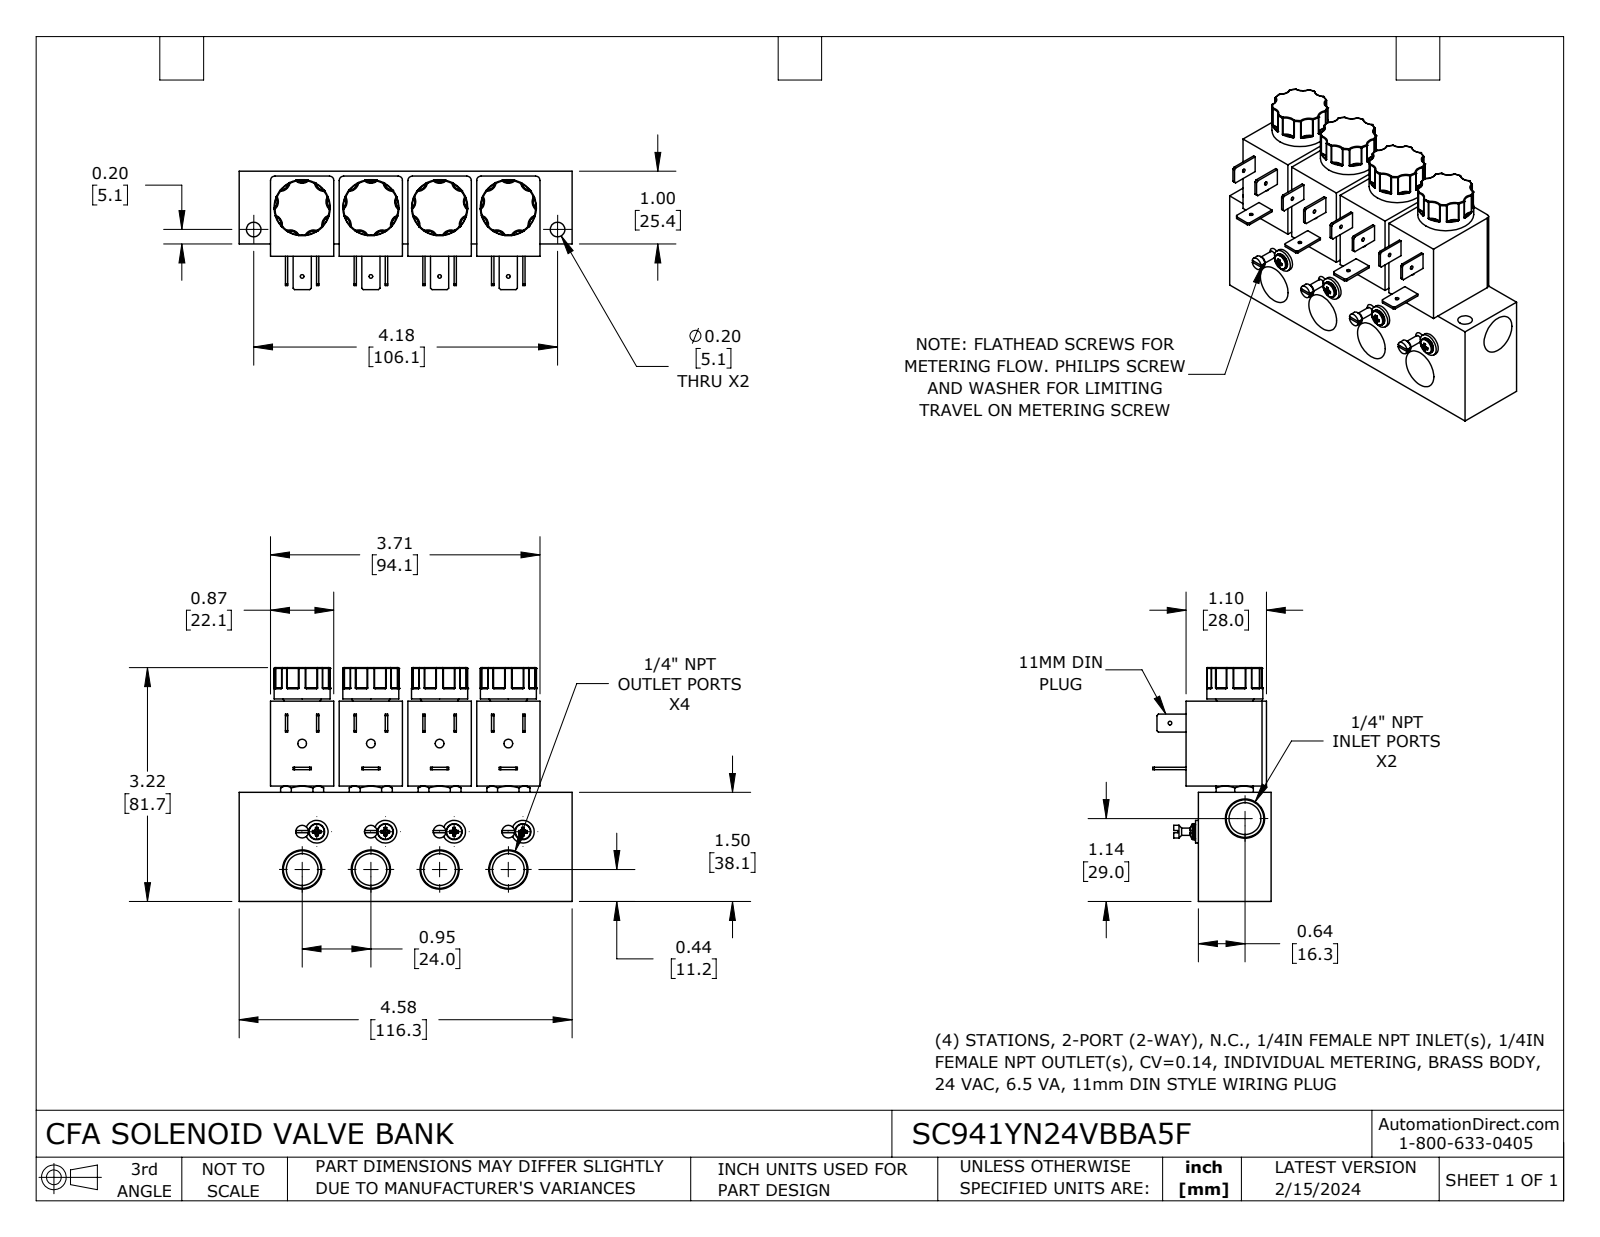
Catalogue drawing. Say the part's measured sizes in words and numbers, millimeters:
The part is named "SC941YN24VBBA5F". Its 3-D file was written by "SolidWorks 2023 (CONFIG_CONTROL_DESIGN)". It is 1 solid with 1098 faces: 284 planar, 260 cylindrical and 554 other. Overall it measures 116.3 by 81.7 by 41.3 millimeters. Its volume is 188 300 cubic millimeters and its surface area 44 010 square millimeters. Round holes: 5 of diameter 1.3, 5 of diameter 11.1, 4 of diameter 3, 2 of diameter 5.1. Round bosses or shafts: 4 of diameter 19.6, 4 of diameter 7.9, 4 of diameter 5.6, 4 of diameter 4.4, 4 of diameter 2.5. Partial cylindrical surfaces (rounded edges, fillets, slot ends): 72 of radius 0.3, 28 of radius 3.4, 8 of radius 1.5, 8 of radius 3.4. The main face-to-face distances are 25.4, 24, 29.7, 4.3, 48, 22.1, 46.1, 38.1, 1.7, 23.7. The hole center spacings are 24, 44, 50.1, 24, 48, 48, 72, 50.1.
